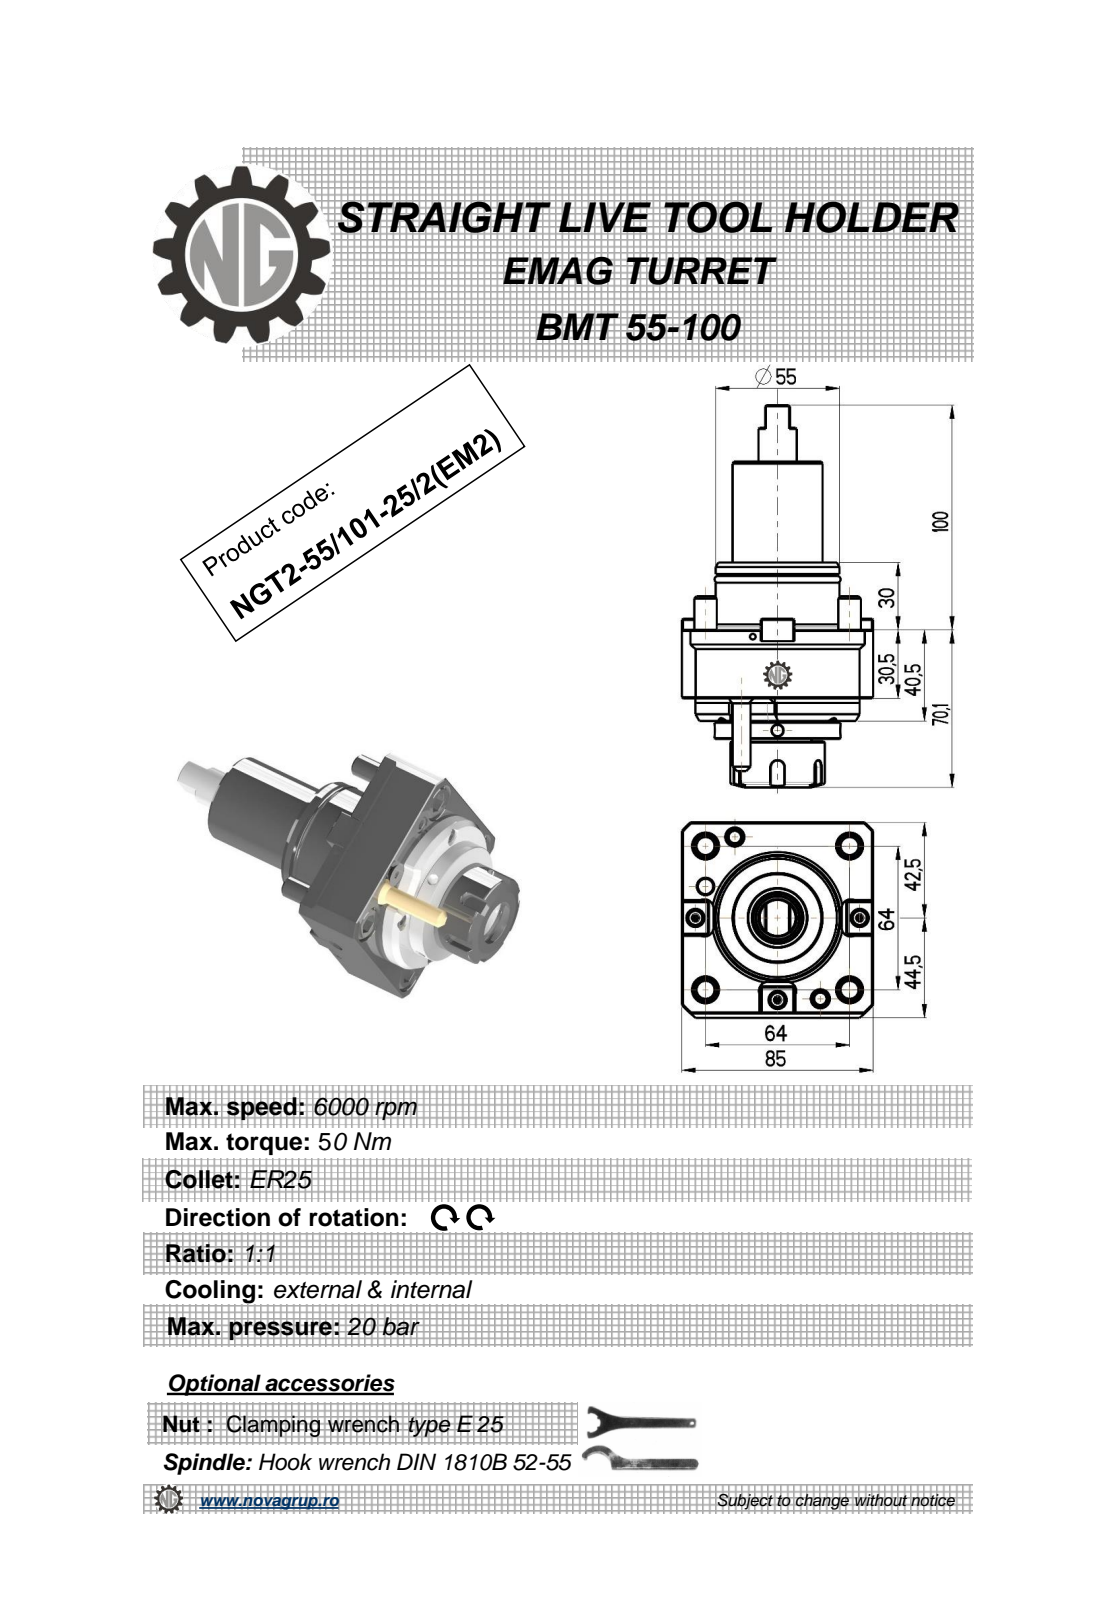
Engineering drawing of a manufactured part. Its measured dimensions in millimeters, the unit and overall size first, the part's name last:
Units: millimetres
Overall size (bounding box): 170.1 × 87 × 85
Round holes (diameter × count): ⌀5 ×3, ⌀3 ×1, ⌀6.8 ×1, ⌀20.3 ×1
Round bosses / shafts (diameter × count): ⌀10 ×4, ⌀73 ×1, ⌀56 ×1, ⌀55 ×1, ⌀54.4 ×1, ⌀50 ×1, ⌀43 ×1, ⌀42 ×1
Partial cylindrical surfaces — rounded edges, fillets, slot ends (radius × count): R0.22 ×6, R3 ×5, R0.8 ×2, R6 ×2, R57.5 ×1
Main face-to-face distances: 30.5, 85, 10, 40.5, 48.5, 87, 8, 18, 10.5, 60.5
Hole centre spacings: 34.93, 37.12, 50.12
Volume: 448 209 mm³ · Surface area: 53 307 mm²
Bodies: 2 solids, 314 faces (140 planar, 67 cylindrical, 107 other)
Part name (STEP PRODUCT): NGT2_55_101_25_1_EM2
STEP written by: PRO/ENGINEER BY PARAMETRIC TECHNOLOGY CORPORATION, 2010280 (CONFIG_CONTROL_DESIGN)
